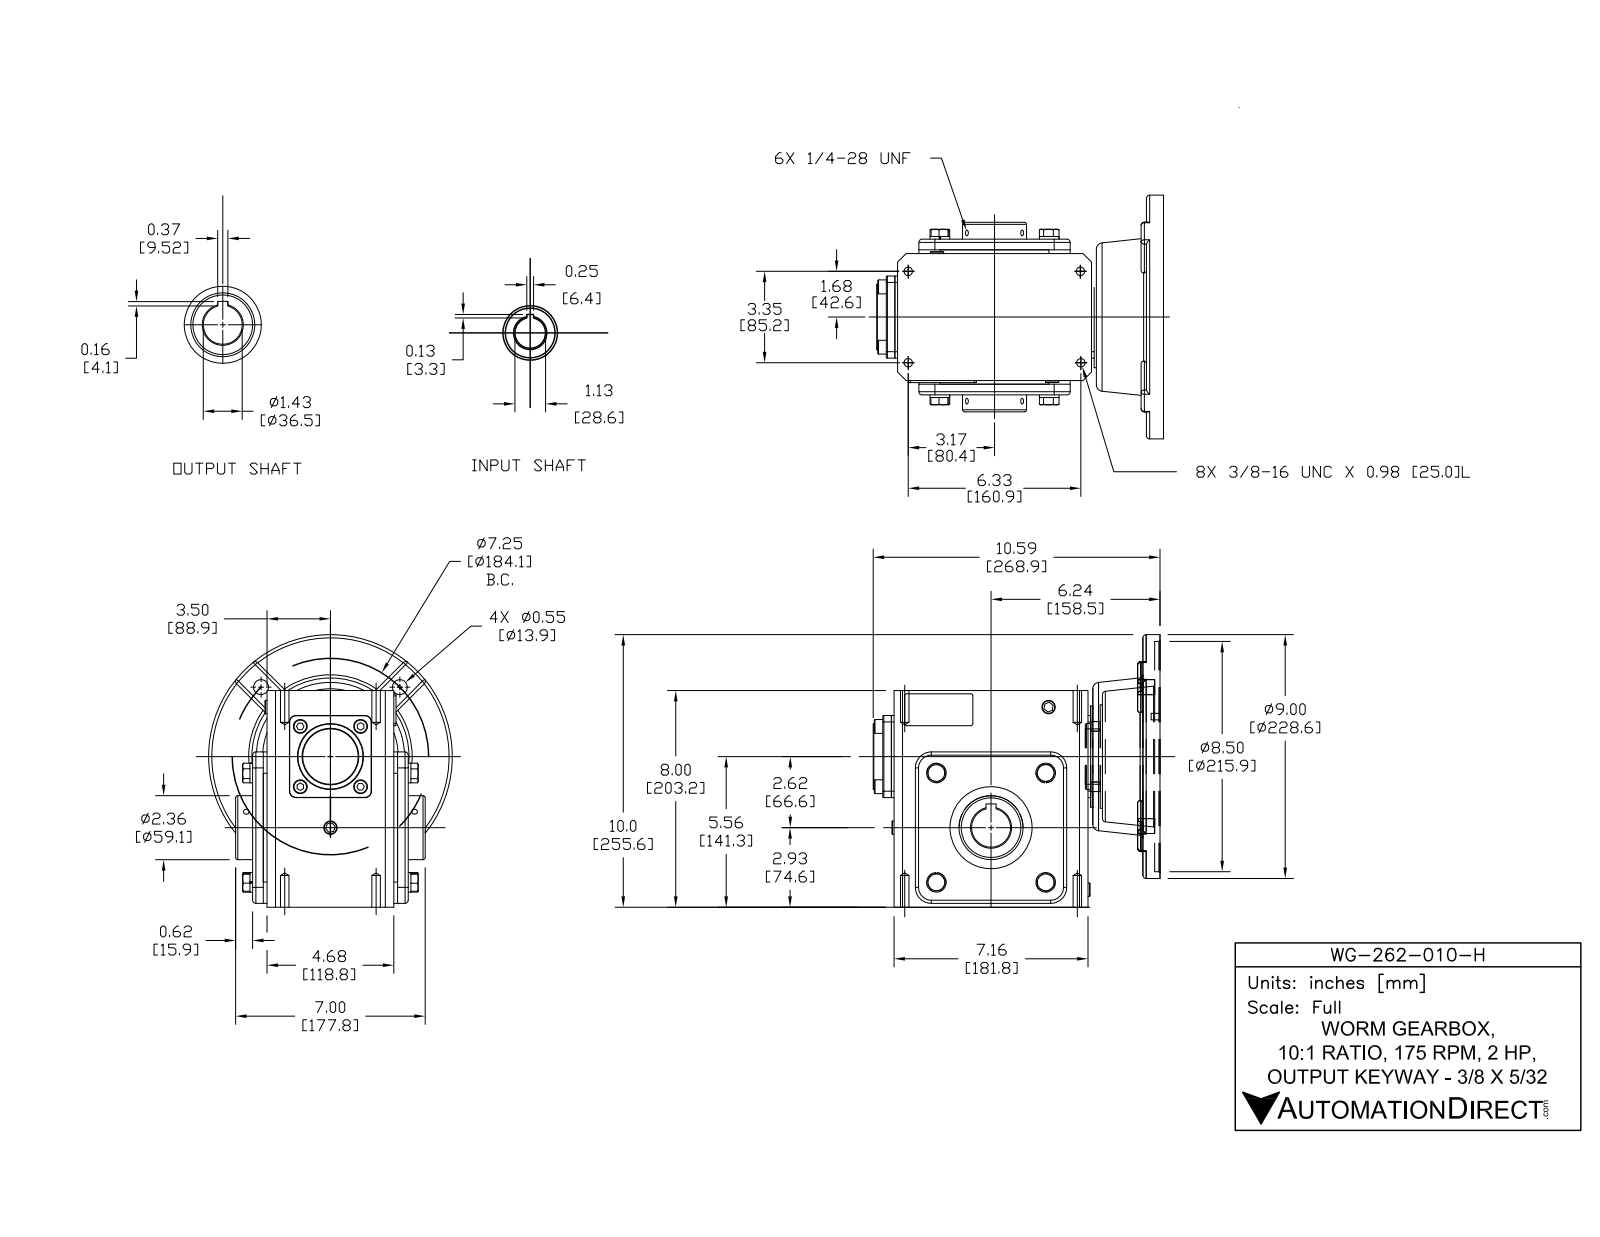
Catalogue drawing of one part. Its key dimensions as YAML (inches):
part_name: "WG-262-010-H"
step_written_by: "SolidWorks 2015 (CONFIG_CONTROL_DESIGN)"
units: inches
bodies: {solids: 32, faces: 553, planar: 277, cylindrical: 160, other: 116}
overall_size: [10.591, 10.063, 9]
volume: 313.4
surface_area: 819.4
round_holes:
  - {diameter: 0.213, count: 6}
  - {diameter: 0.313, count: 4}
  - {diameter: 0.551, count: 4}
  - {diameter: 0.591, count: 1}
  - {diameter: 1.125, count: 1}
  - {diameter: 1.437, count: 1}
  - {diameter: 2.047, count: 1}
  - {diameter: 2.362, count: 1}
  - {diameter: 3.031, count: 1}
  - {diameter: 3.819, count: 1}
  - {diameter: 8.5, count: 1}
round_bosses_or_shafts:
  - {diameter: 0.724, count: 4}
  - {diameter: 0.512, count: 4}
  - {diameter: 9, count: 1}
  - {diameter: 3.74, count: 1}
  - {diameter: 2.441, count: 1}
  - {diameter: 1.772, count: 1}
  - {diameter: 1.142, count: 1}
partial_cylinders:
  - {radius: 0.118, count: 20}
  - {radius: 0.079, count: 6}
  - {radius: 0.236, count: 4}
  - {radius: 0.591, count: 4}
  - {radius: 0.787, count: 4}
  - {radius: 0.02, count: 2}
  - {radius: 0.039, count: 2}
face_to_face_distances: [4.961, 0.394, 0.531, 5.217, 5.354, 0.138, 4.823, 8, 0.433, 2.028]
hole_center_spacings: [3.489, 3.625, 5.127, 5.757, 6.213, 2.564, 3.375, 5.787]
